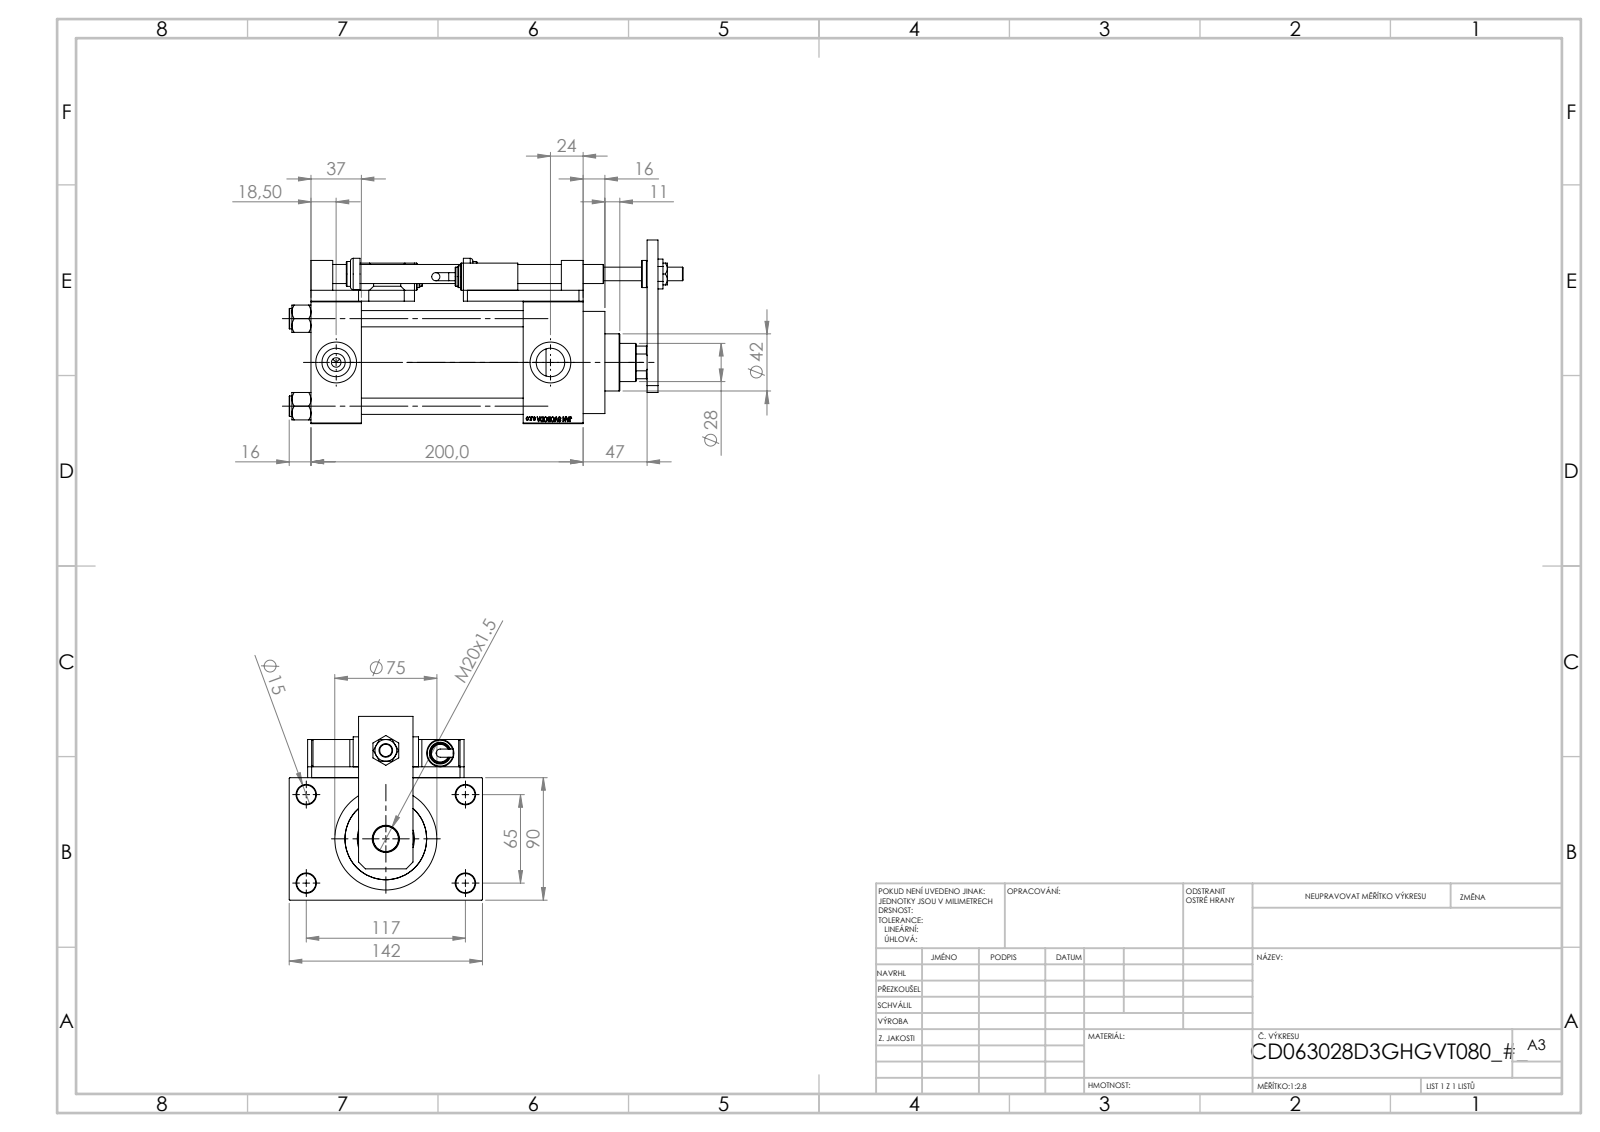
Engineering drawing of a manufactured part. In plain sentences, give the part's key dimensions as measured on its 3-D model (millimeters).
The part is named "V215CD_VCP_D; V215CD_SWITCH_Q_BLOK; V215CD_SWITCH_Q_TYC; V215CD_VC_A (+7 more)". Its 3-D file was written by "SolidWorks 2019 (CONFIG_CONTROL_DESIGN)". It is 26 solids with 1432 faces: 666 planar, 167 cylindrical and 599 other. Overall it measures 289.5 by 142 by 135 millimeters. Its volume is 1 467 000 cubic millimeters and its surface area 332 028 square millimeters. Round holes: 5 of diameter 14, 4 of diameter 8.5, 4 of diameter 12, 4 of diameter 13.5, 4 of diameter 20.96, 4 of diameter 30, 3 of diameter 7, 1 of diameter 10, 1 of diameter 18.5, 1 of diameter 20, 1 of diameter 28, 1 of diameter 31. Round bosses or shafts: 4 of diameter 15, 3 of diameter 20, 2 of diameter 16, 2 of diameter 14, 2 of diameter 6, 1 of diameter 75, 1 of diameter 69, 1 of diameter 42. Partial cylindrical surfaces (rounded edges, fillets, slot ends): 4 of radius 7.5, 1 of radius 13.5. The main face-to-face distances are 8, 90, 44, 200, 37, 98, 163, 156, 119, 47. The hole center spacings are 66.92, 26.35, 45.47, 64.3, 69.81, 90.65, 111.34, 65.
